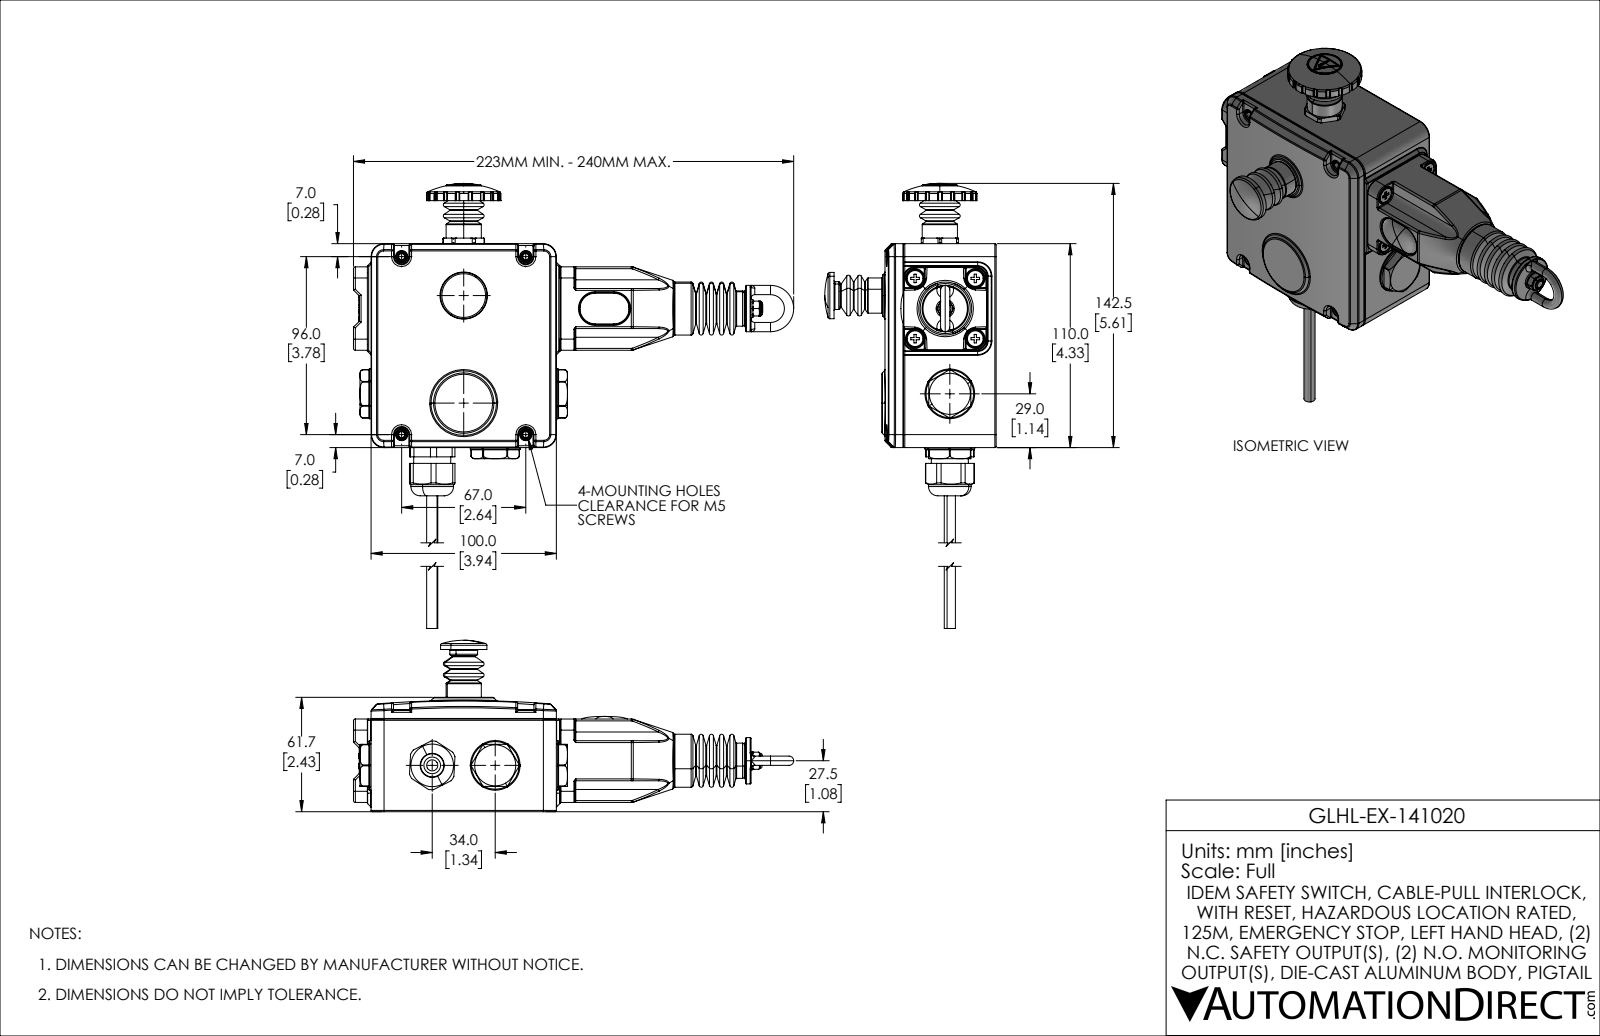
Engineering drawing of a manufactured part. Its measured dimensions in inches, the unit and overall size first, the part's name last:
Units: inches
Overall size (bounding box): 9.354 × 9.193 × 3.642
Round holes (diameter × count): ⌀0.197 ×11, ⌀0.209 ×9, ⌀0.354 ×7, ⌀0.374 ×7, ⌀0.13 ×4, ⌀0.157 ×4, ⌀0.189 ×4, ⌀0.213 ×4, ⌀0.228 ×4, ⌀0.118 ×3, ⌀0.173 ×3, ⌀0.083 ×2
Round bosses / shafts (diameter × count): ⌀0.236 ×8, ⌀0.335 ×4, ⌀0.173 ×4, ⌀0.748 ×3, ⌀0.197 ×3, ⌀1.055 ×2, ⌀0.984 ×2, ⌀0.764 ×2
Partial cylindrical surfaces — rounded edges, fillets, slot ends (radius × count): R0.02 ×220, R0.039 ×130, R0.008 ×88, R0.028 ×64, R0.012 ×20, R0.006 ×14, R0.236 ×12, R0.004 ×11
Main face-to-face distances: 2.157, 0.138, 0.114, 2.043, 4.331, 0.055, 0.157, 0.079, 3.878, 4.016
Hole centre spacings: 1.28, 0.374, 0.905, 1.891, 1.913, 3.012, 3.489, 3.78
Volume: 18.53 in³ · Surface area: 281.3 in²
Bodies: 27 solids, 3744 faces (969 planar, 1210 cylindrical, 1565 other)
Part name (STEP PRODUCT): GLHL-EX-141020
STEP written by: SolidWorks 2021 (AUTOMOTIVE_DESIGN)
